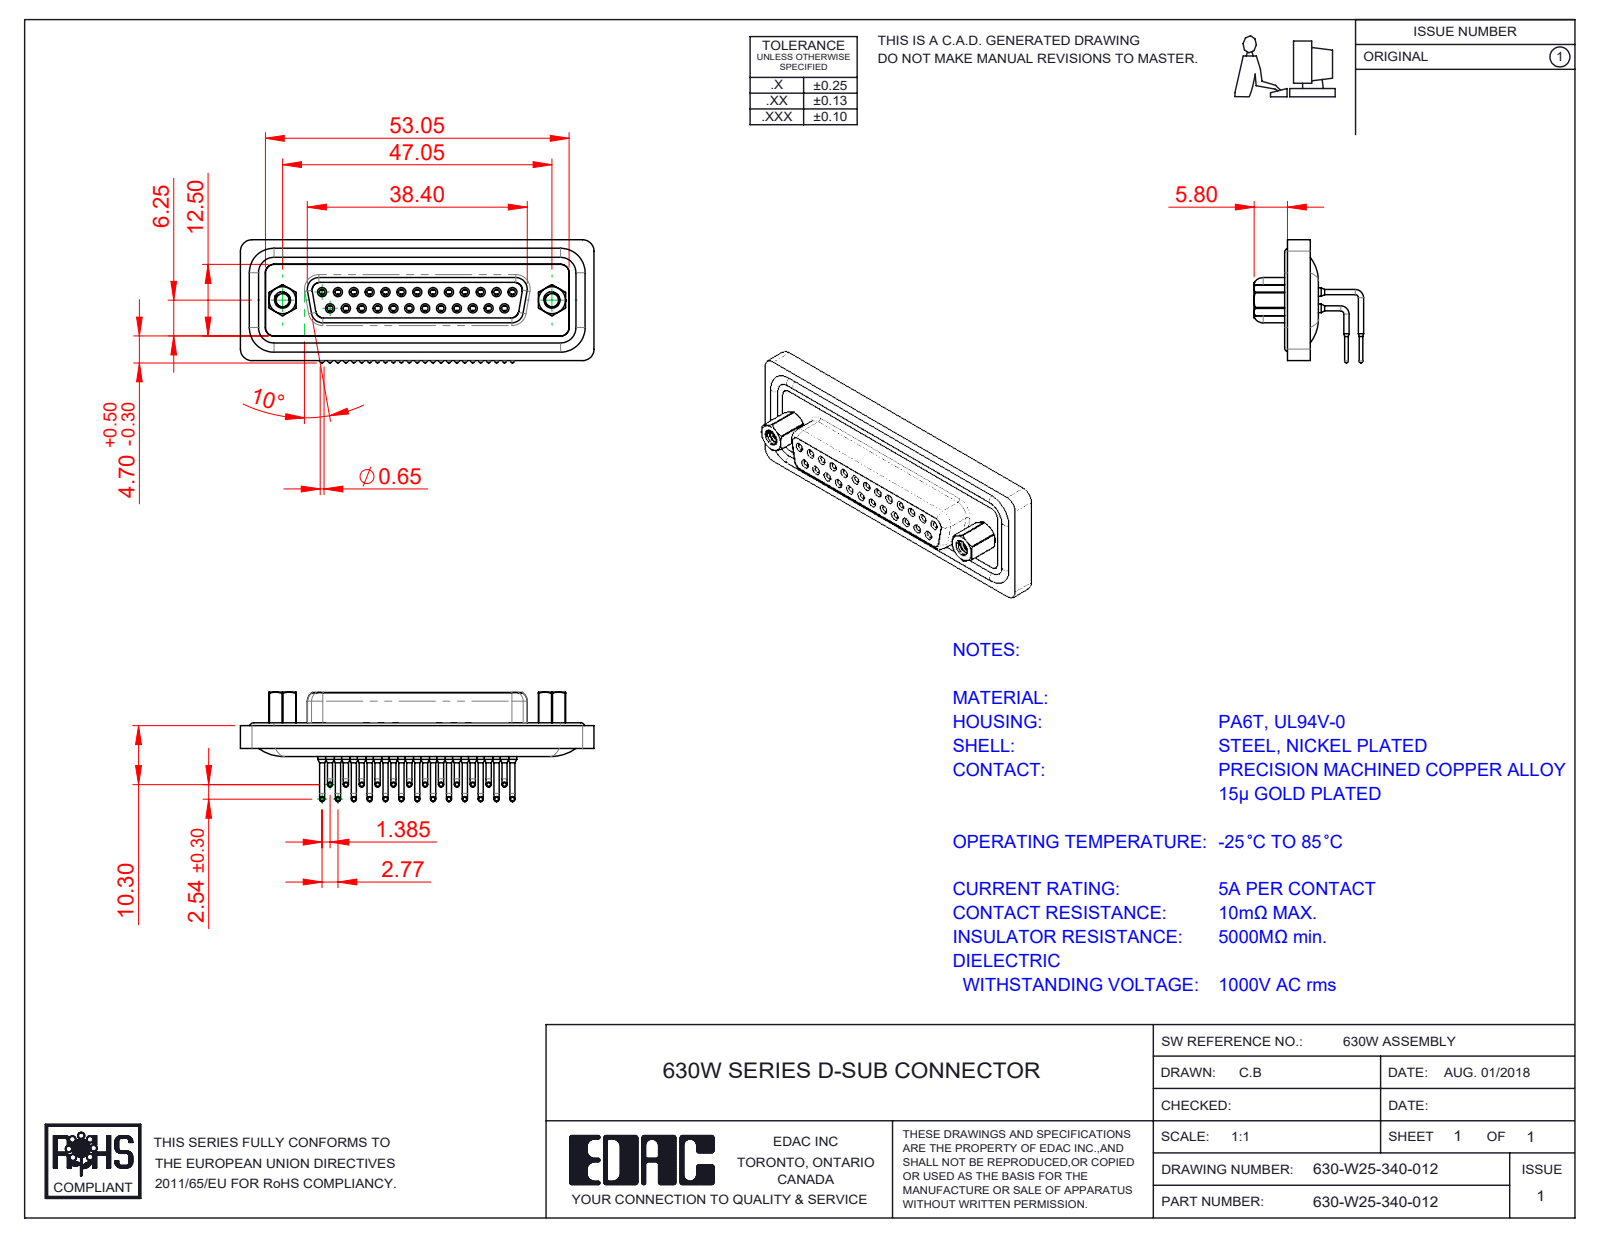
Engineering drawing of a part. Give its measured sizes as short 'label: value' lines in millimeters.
name: 630W 4-40 Hex Standoff; 630-W25-340-012; 630W 4-40 Threaded Rivet_Stabilizer; 630W Contact Row 2 (+4 more)
written by: SolidWorks 2016 (CONFIG_CONTROL_DESIGN)
unit: mm
bodies: 33 solids, 1790 faces (476 planar, 837 cylindrical, 477 other)
size: 61.74 × 21.5 × 19.14
volume: 7 468 mm³; area: 13 495 mm²
holes: 25× ⌀1, 25× ⌀1.1, 25× ⌀1.5, 25× ⌀1.7, 25× ⌀1.8, 25× ⌀2, 2× ⌀2.26, 2× ⌀2.29, 2× ⌀4, 2× ⌀4.8, 2× ⌀5
bosses: 50× ⌀0.9, 29× ⌀1.6, 25× ⌀0.65, 2× ⌀4.9, 2× ⌀2.79, 1× ⌀5
rounds: 14× R1.5, 14× R2, 8× R1.35, 6× R2.7, 4× R0.5, 4× R0.9, 4× R1.6, 4× R1.75
face distances: 0.4, 1.8, 1.6, 1.1, 2.5, 2.9, 7.45, 13.65, 9.8, 6.2
hole spacings: 3.16, 2.77, 5.54, 8.31, 11.08, 13.85, 16.62, 5.03
